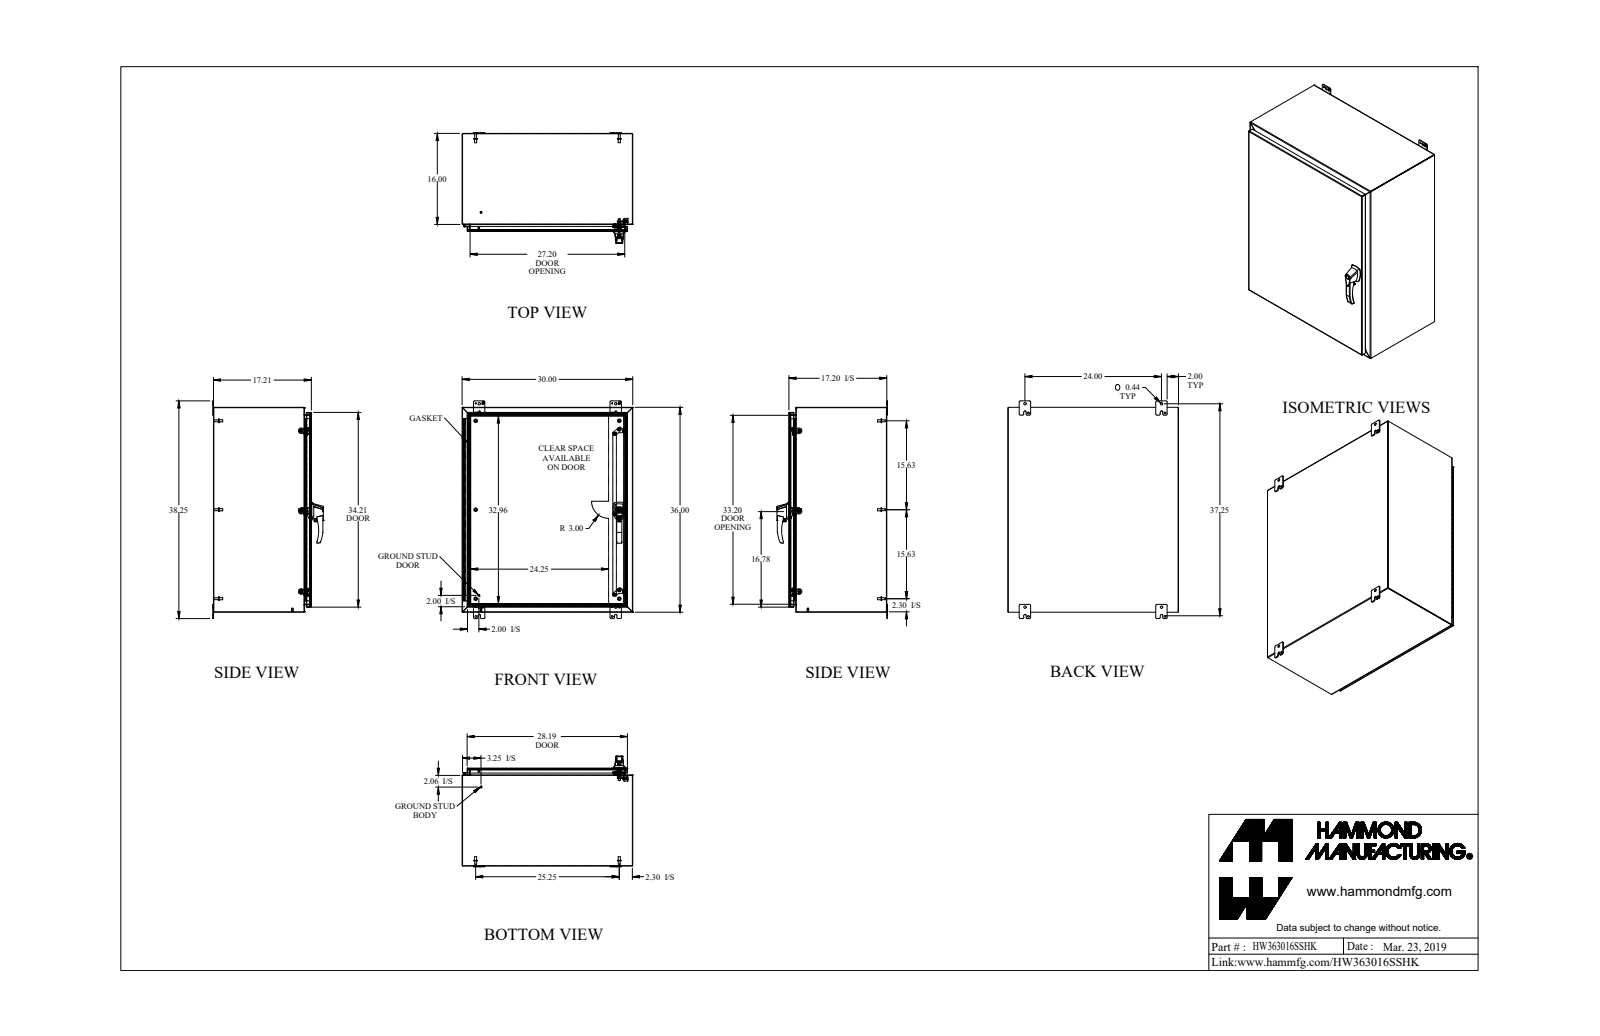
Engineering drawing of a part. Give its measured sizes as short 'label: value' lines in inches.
name: HW363016SSHK
written by: SolidWorks 2018 (AUTOMOTIVE_DESIGN)
unit: in
bodies: 46 solids, 1509 faces (721 planar, 630 cylindrical, 158 other)
size: 38.25 × 30 × 19.45
volume: 369.4 in³; area: 9 843 in²
holes: 6× ⌀0.176, 5× ⌀0.313, 3× ⌀0.25, 3× ⌀0.265, 3× ⌀0.413, 2× ⌀0.196, 2× ⌀0.256, 2× ⌀0.394, 2× ⌀0.437, 1× ⌀0.187, 1× ⌀0.233, 1× ⌀0.33
bosses: 11× ⌀0.375, 7× ⌀0.25, 6× ⌀0.65, 6× ⌀0.332, 6× ⌀0.156, 3× ⌀1, 3× ⌀0.51, 2× ⌀0.63
rounds: 27× R0.25, 24× R0.188, 18× R0.036, 18× R0.108, 12× R0.06, 9× R0.125, 8× R0.045, 8× R0.218
face distances: 0.072, 29.928, 0.072, 17.138, 17.066, 17.138, 17.21, 35.928, 29.856, 30
hole spacings: 14.118, 14.119, 28.237, 1.11, 1.111, 14.119, 24, 24.724
